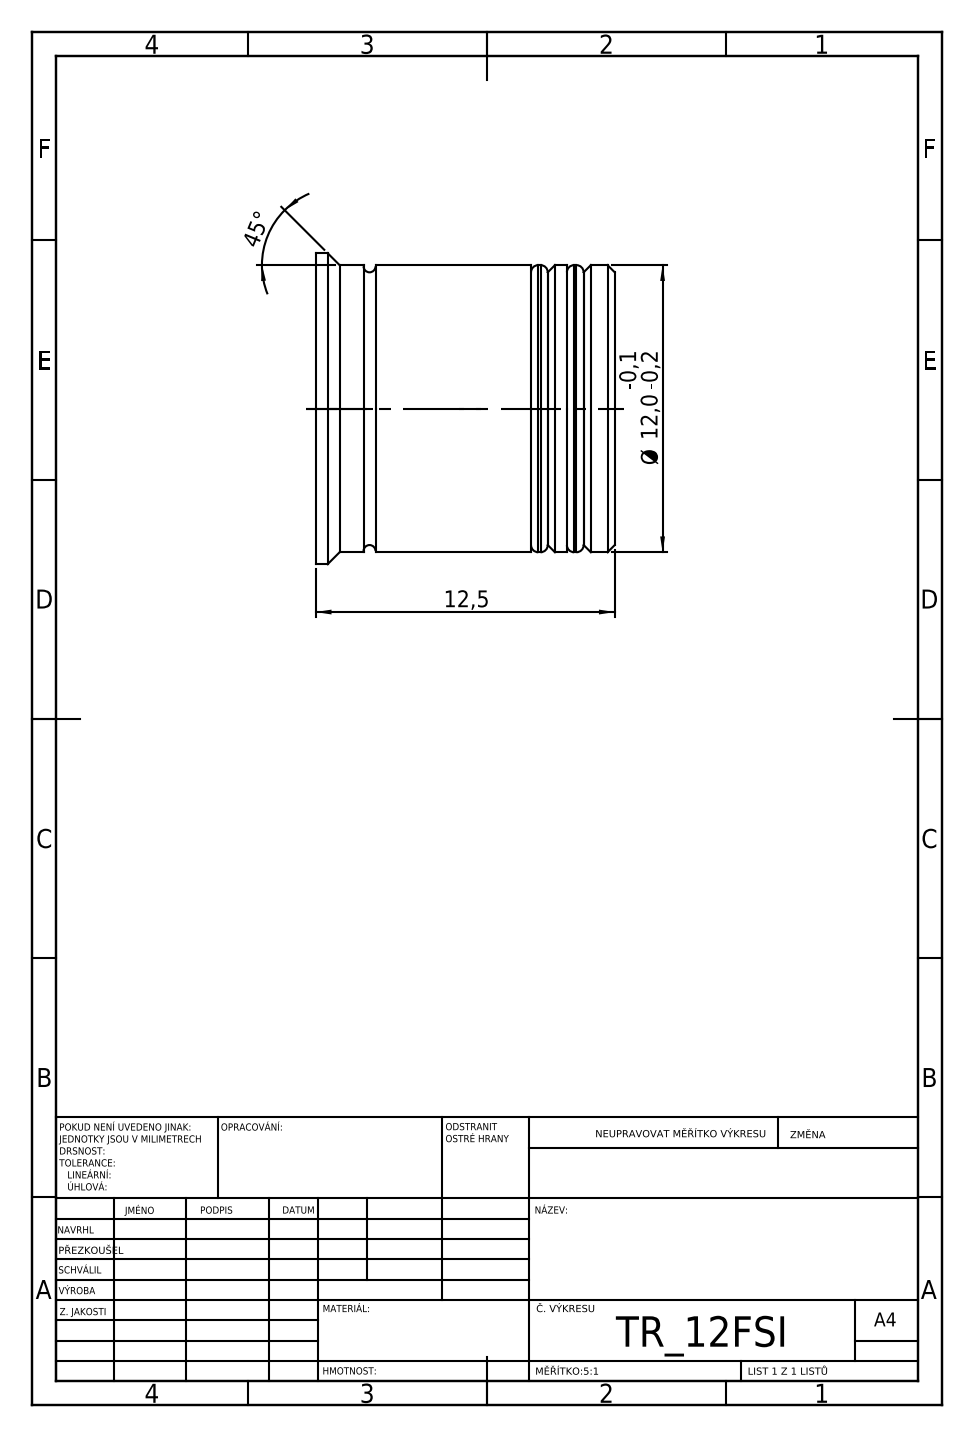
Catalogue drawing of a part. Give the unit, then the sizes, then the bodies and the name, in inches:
Units: inches
Overall size (bounding box): 0.512 × 0.512 × 0.492
Round bosses / shafts (diameter × count): ⌀0.512 ×1, ⌀0.472 ×1, ⌀0.449 ×1, ⌀0.354 ×1
Main face-to-face distances: 0.059, 0.028, 0.079, 0.087, 0.031, 0.051, 0.11, 0.138, 0.315, 0.039
Volume: 0.09 in³ · Surface area: 2.066 in²
Bodies: 3 solids, 74 faces (29 planar, 25 cylindrical, 20 other)
STEP written by: SolidWorks 2019 (CONFIG_CONTROL_DESIGN)
